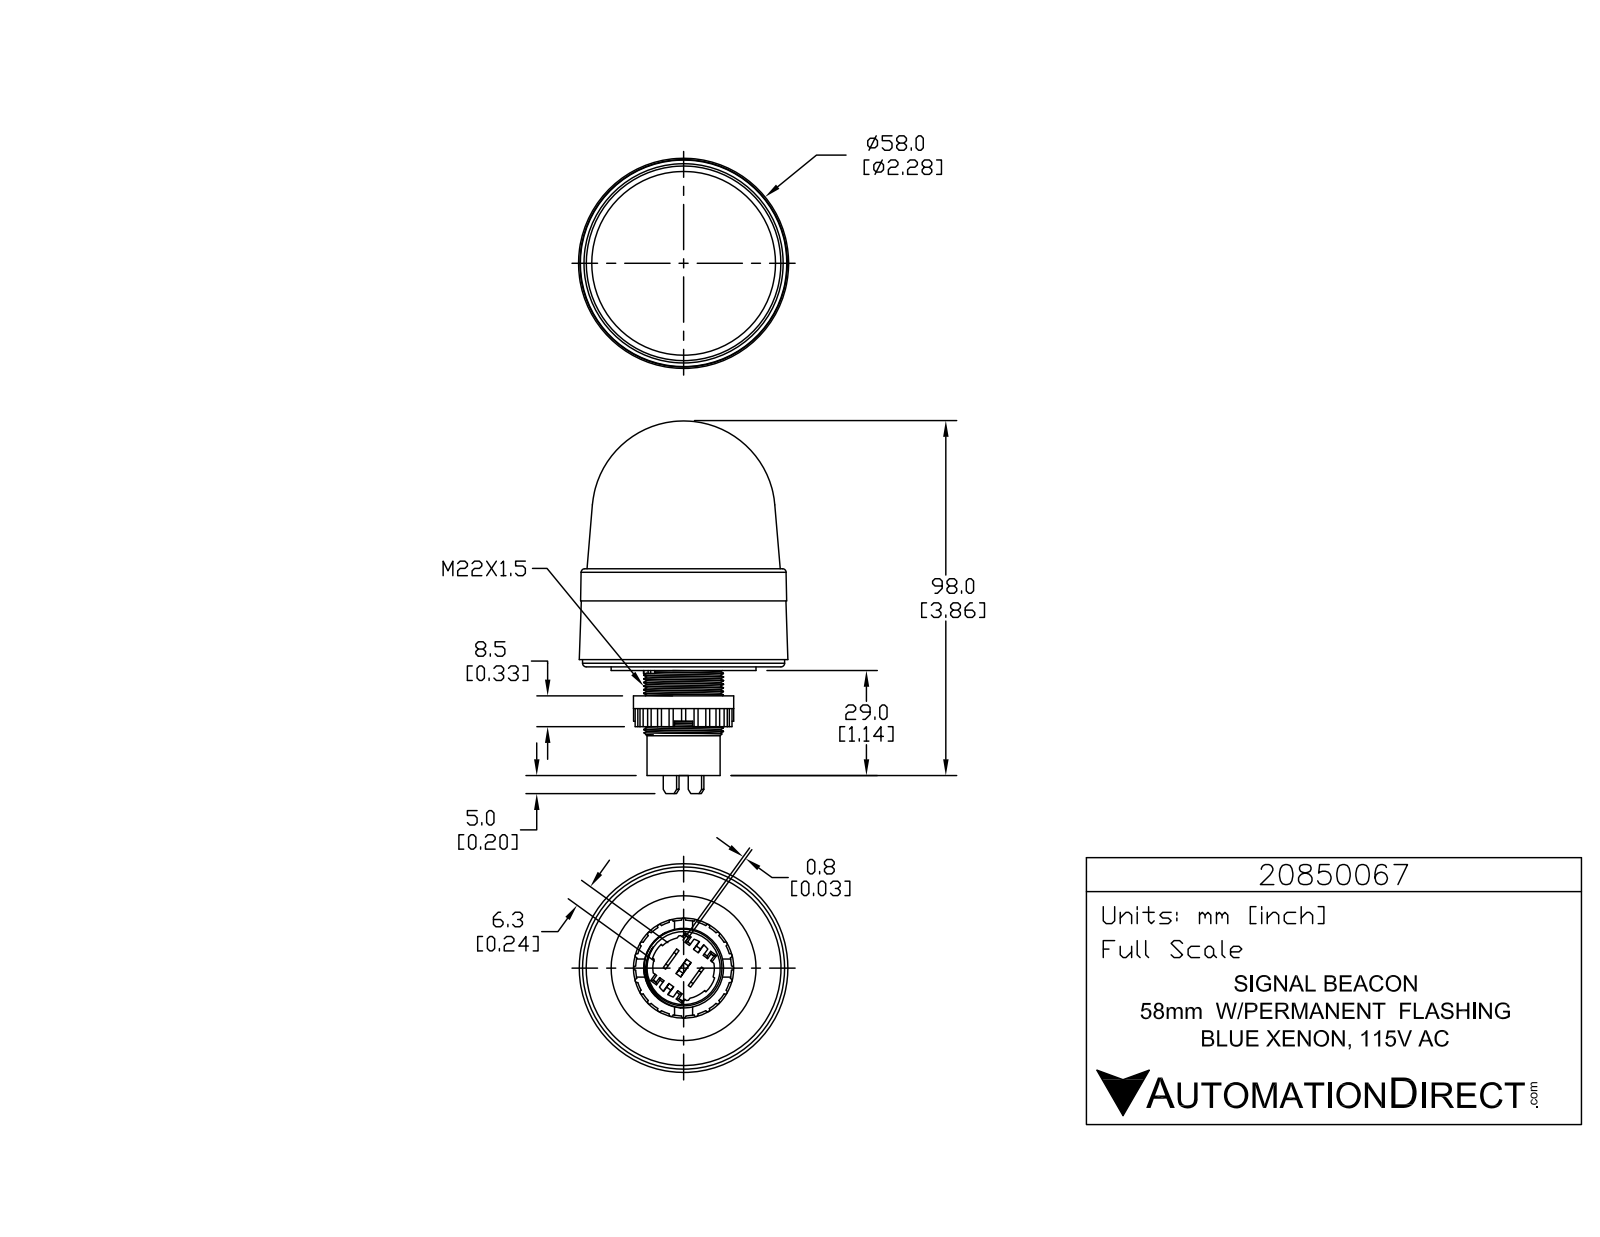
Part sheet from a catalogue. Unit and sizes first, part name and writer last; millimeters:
Units: millimetres
Overall size (bounding box): 102.9 × 57.6 × 57.6
Round holes (diameter × count): ⌀23 ×1
Round bosses / shafts (diameter × count): ⌀55.8 ×1, ⌀40 ×1, ⌀27.7 ×1, ⌀22 ×1, ⌀20.2 ×1
Partial cylindrical surfaces — rounded edges, fillets, slot ends (radius × count): R0.6 ×24, R0.5 ×2, R8.5 ×1, R9 ×1, R13.3 ×1
Main face-to-face distances: 1, 7, 3, 29, 8.5, 8, 27, 19, 26, 18.5
Volume: 147 700 mm³ · Surface area: 20 030 mm²
Bodies: 1 solid, 266 faces (119 planar, 120 cylindrical, 27 other)
Part name (STEP PRODUCT): 20850067
STEP written by: SolidWorks 2015 (AUTOMOTIVE_DESIGN)
